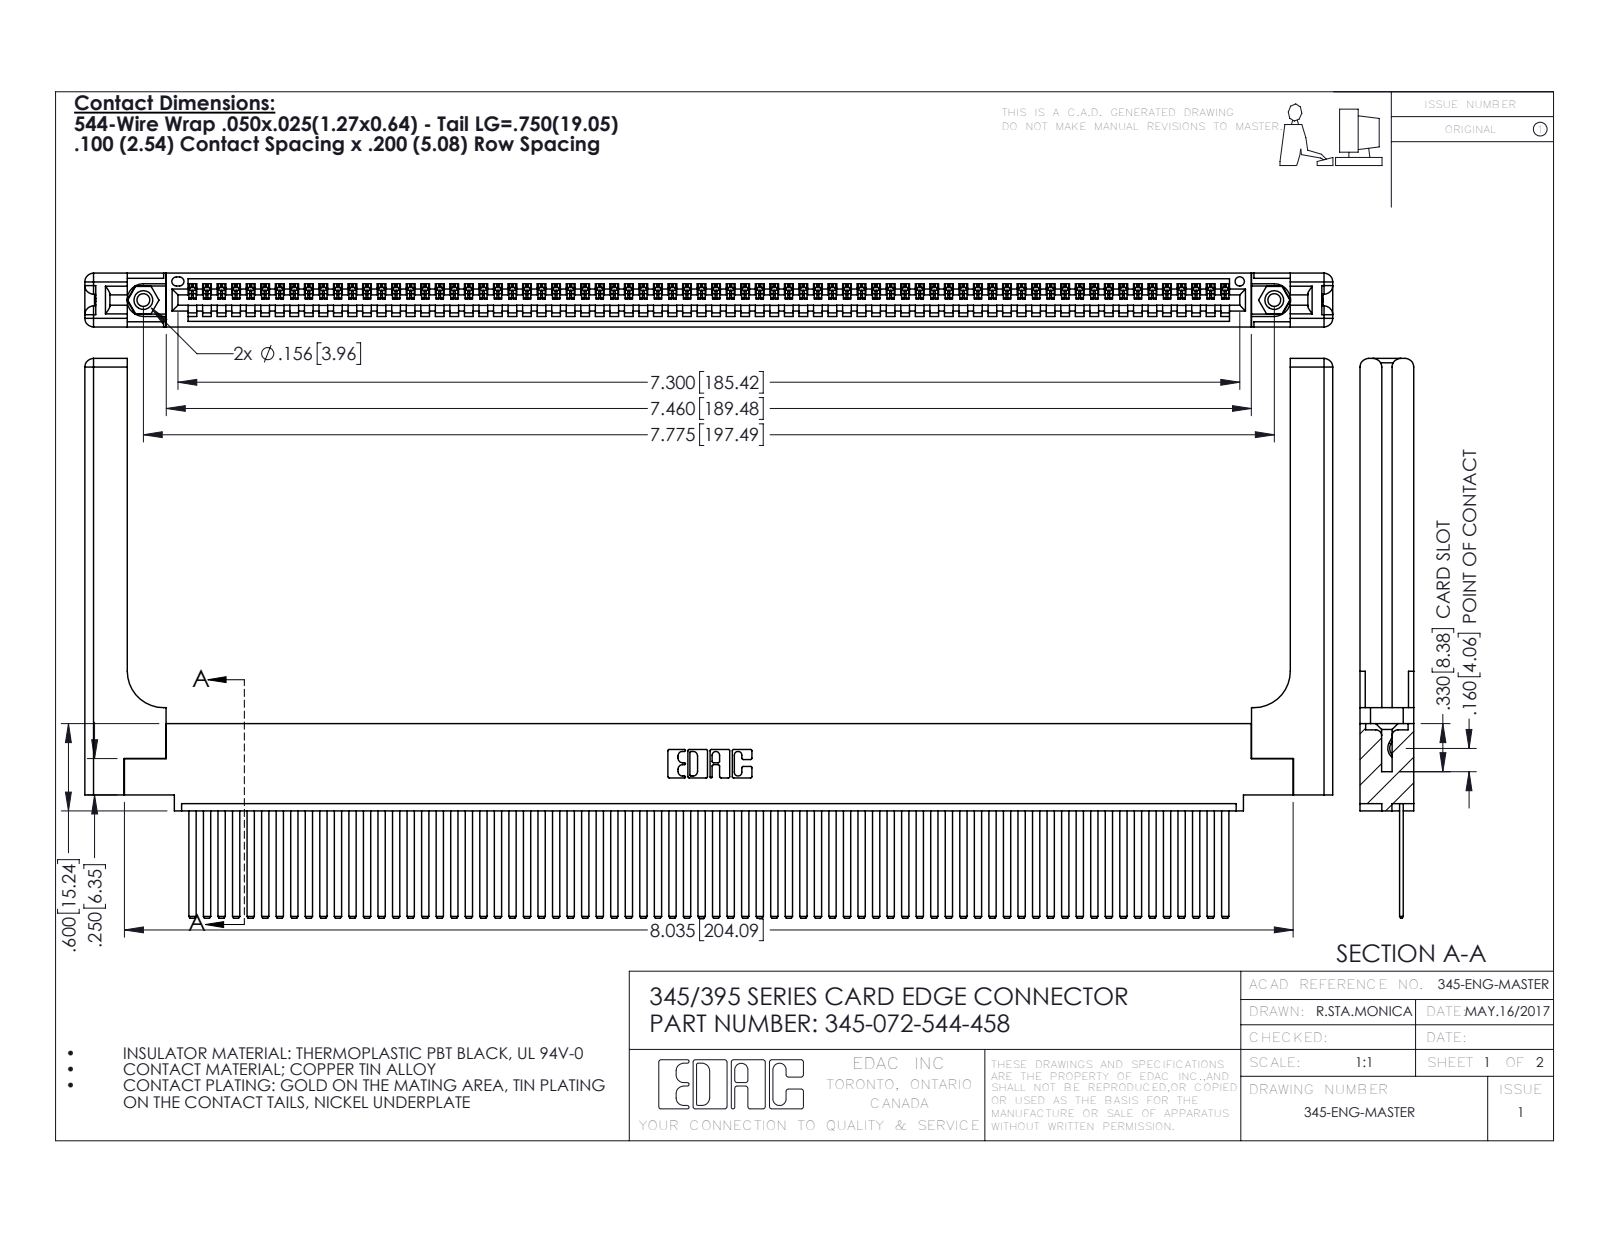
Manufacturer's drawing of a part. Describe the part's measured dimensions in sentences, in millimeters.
The part is named "345-250-001_345-250-001-102; 345-220-058_345-220-058; 345 Part_0.110 Offset - 0.156 Dia-TH; 345-292-001_345-293-144 (+1 more)". Its 3-D file was written by "SolidWorks 2016 (CONFIG_CONTROL_DESIGN)". It is 77 solids with 4130 faces: 2824 planar, 1246 cylindrical and 60 other. Overall it measures 217.9 by 97.7 by 9.4 millimeters. Its volume is 30 200 cubic millimeters and its surface area 37 140 square millimeters. Round holes: 2 of diameter 2.3, 2 of diameter 3.2, 2 of diameter 4, 1 of diameter 1.6. Round bosses or shafts: 2 of diameter 3.9. Partial cylindrical surfaces (rounded edges, fillets, slot ends): 144 of radius 0.2, 22 of radius 0.3, 16 of radius 1.5, 6 of radius 0.2, 6 of radius 0.8, 3 of radius 0.7, 2 of radius 0.8, 2 of radius 0.8. The main face-to-face distances are 1.8, 7.6, 2.5, 6.9, 0.6, 9.4, 5.1, 5.7, 3.8, 3.8. The hole center spacings are 6.9, 191.5, 197.5.
